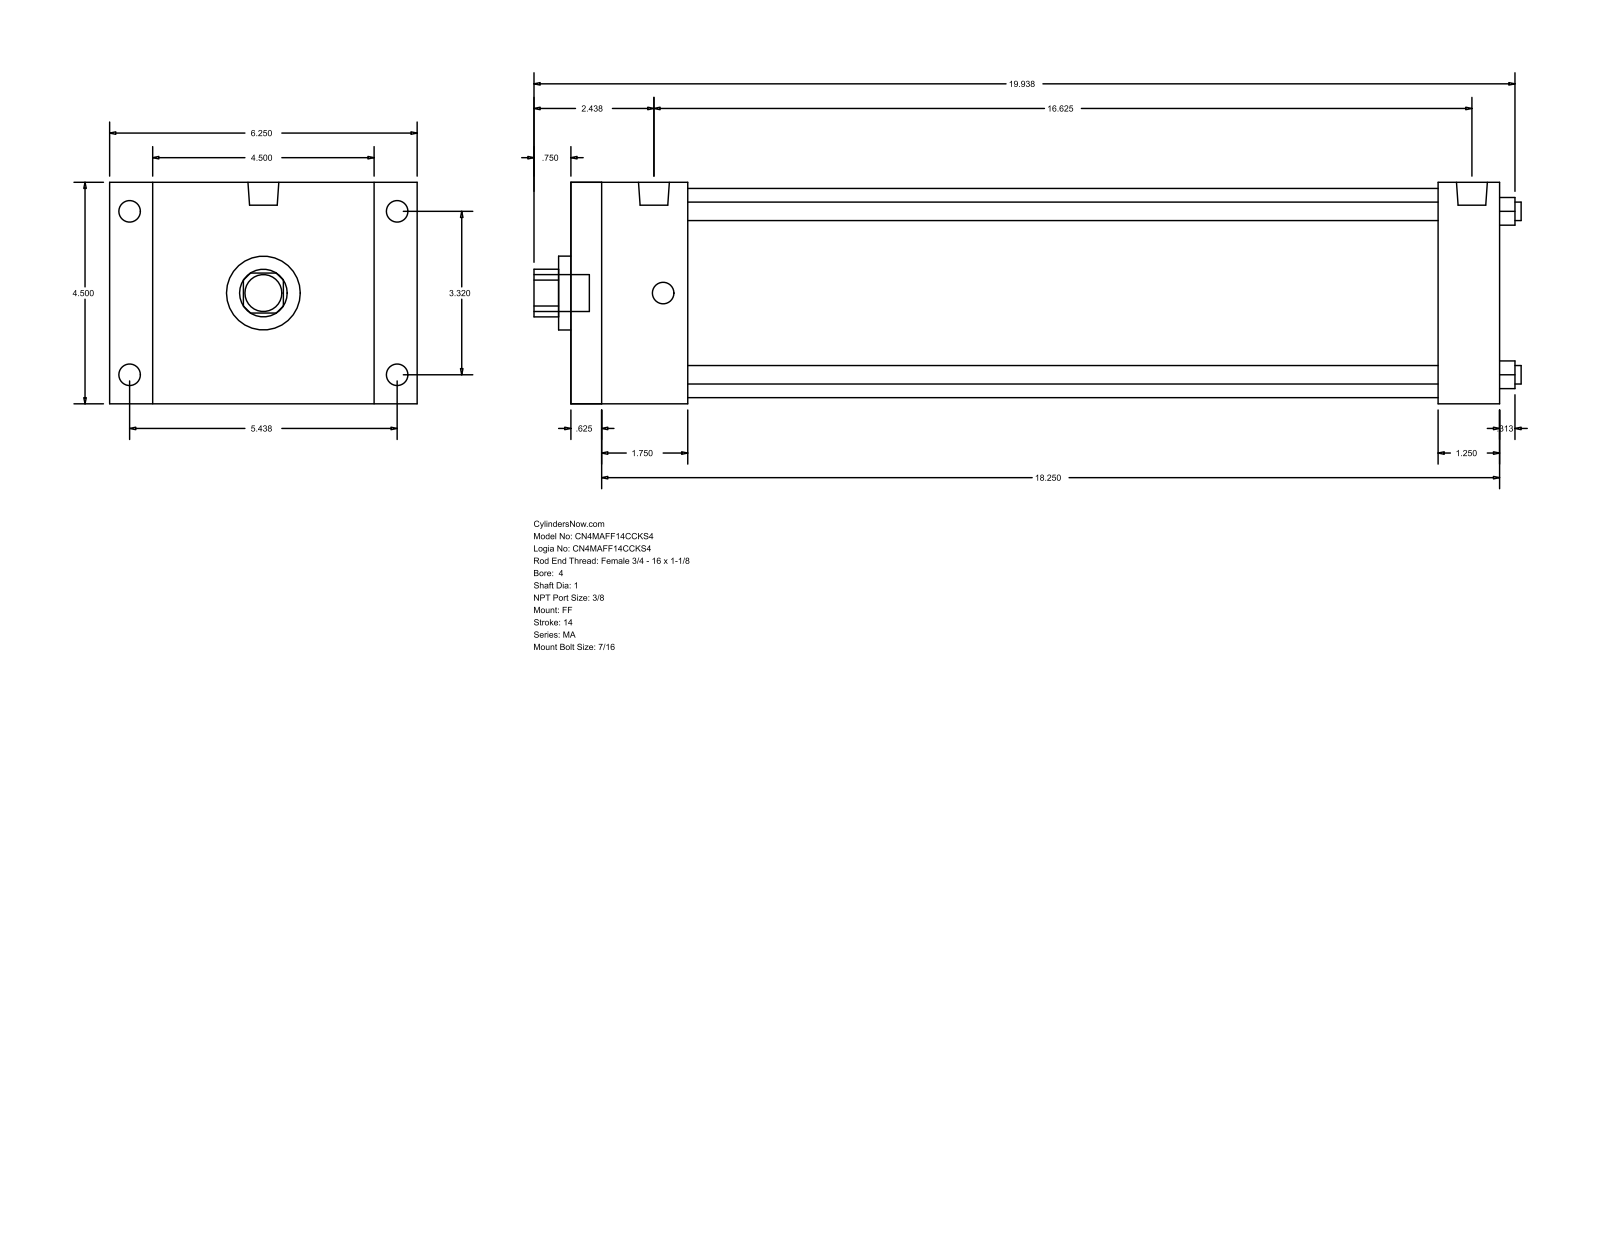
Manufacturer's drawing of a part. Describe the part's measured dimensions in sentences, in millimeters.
The part is named "MA_FF__0400_1". Its 3-D file was written by "GSSL Pune (CONFIG_CONTROL_DESIGN)". It is 0 solids with 92 faces: 64 planar, 28 cylindrical and 0 other. Overall it measures 509.59 by 158.75 by 114.3 millimeters. Round holes: 4 of diameter 9.53, 1 of diameter 25.4, 1 of diameter 38.1, 1 of diameter 107.95. Round bosses or shafts: 8 of diameter 11.11, 2 of diameter 15.93, 1 of diameter 19.05. Partial cylindrical surfaces (rounded edges, fillets, slot ends): 1 of radius 12.29. The main face-to-face distances are 114.3, 479.43, 15.87, 463.56, 22.23, 136.53, 447.68, 431.81, 31.75, 60.33. The hole center spacings are 59.62, 84.32, 119.25.
